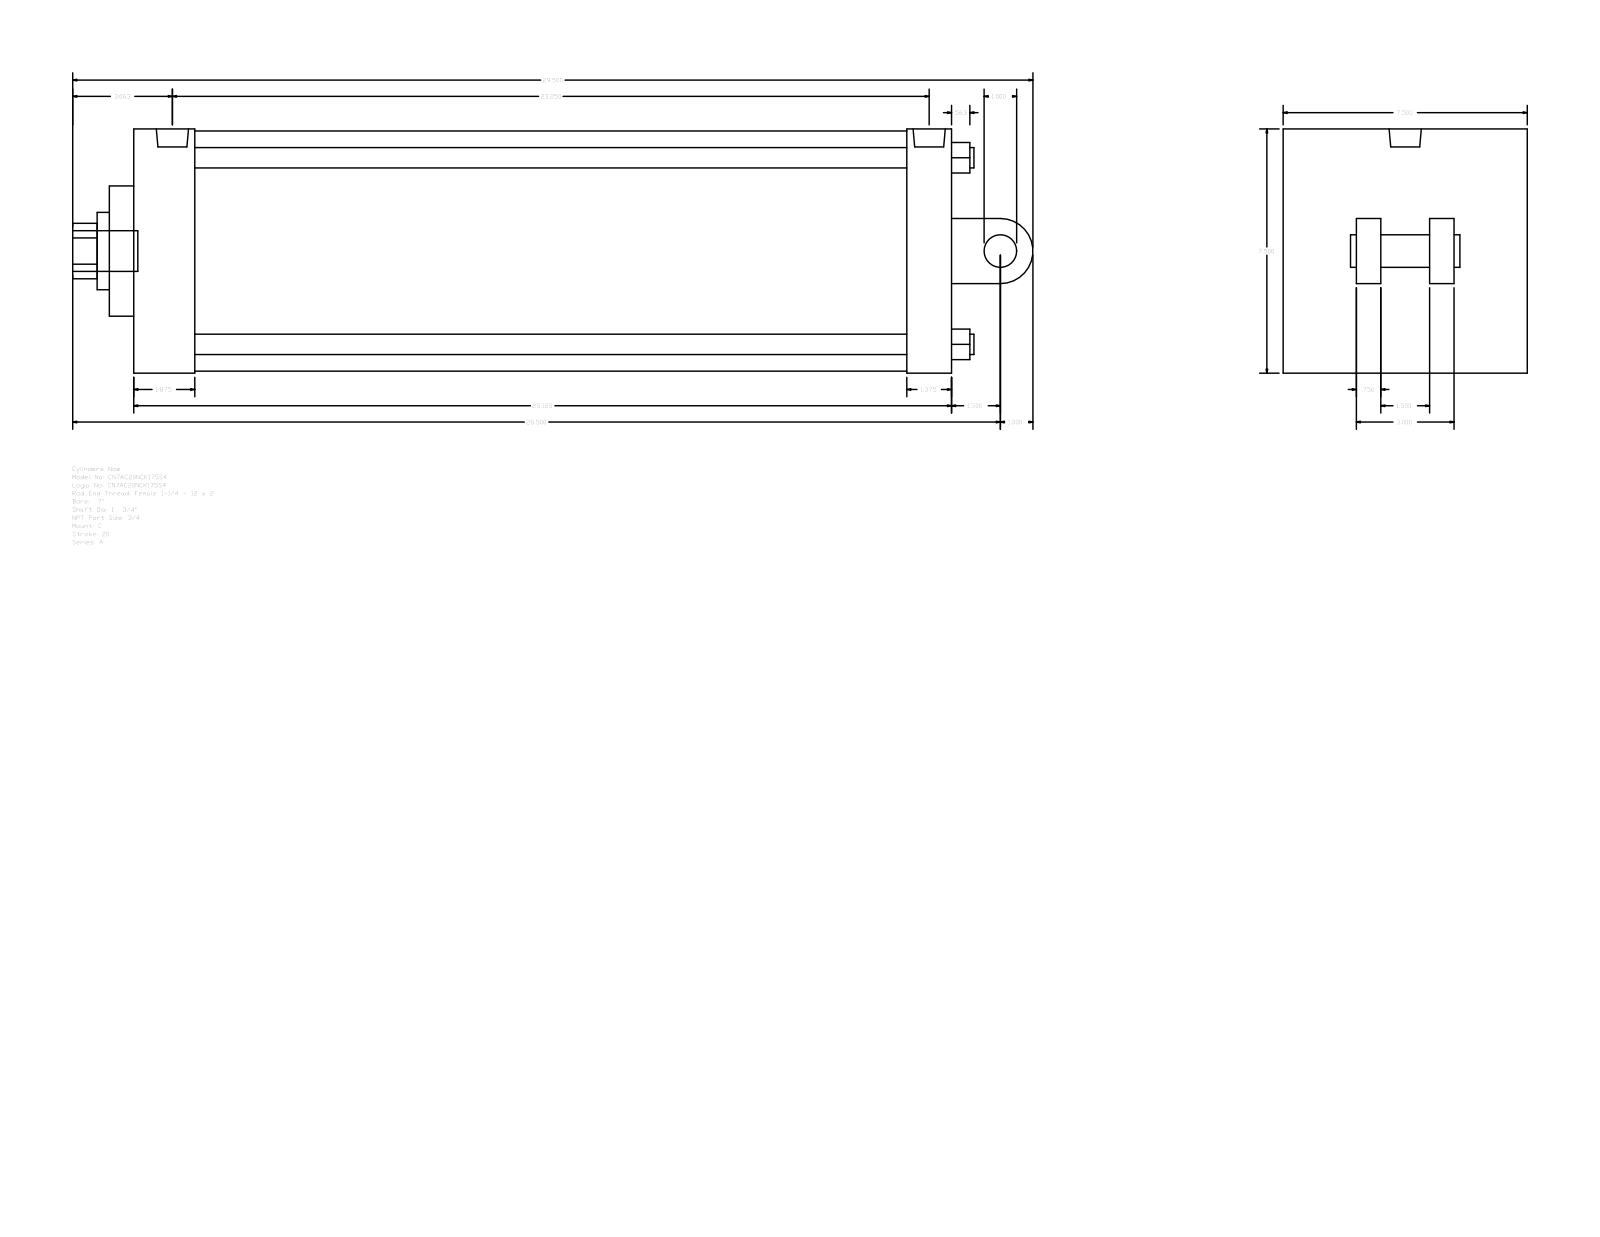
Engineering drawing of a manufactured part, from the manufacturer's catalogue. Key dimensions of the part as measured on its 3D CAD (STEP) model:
Part name (STEP PRODUCT): A_C__0700_1.75
STEP written by: GSSL Pune (CONFIG_CONTROL_DESIGN)
Units: millimetres
Bodies: 0 solids, 104 faces (75 planar, 29 cylindrical, 0 other)
Overall size (bounding box): 749.3 × 190.5 × 190.5
Round holes (diameter × count): ⌀15.88 ×4, ⌀15.08 ×2, ⌀25.12 ×1, ⌀44.45 ×1, ⌀60.33 ×1, ⌀187.32 ×1
Round bosses / shafts (diameter × count): ⌀15.08 ×2, ⌀31.75 ×1, ⌀25.4 ×1, ⌀25.12 ×1
Partial cylindrical surfaces — rounded edges, fillets, slot ends (radius × count): R21.63 ×1, R25.4 ×1
Main face-to-face distances: 190.5, 638.18, 19.05, 76.2, 57.15, 44.45, 34.92, 47.63, 590.55, 603.26
Hole centre spacings: 102.91, 145.54, 205.82, 5.56
